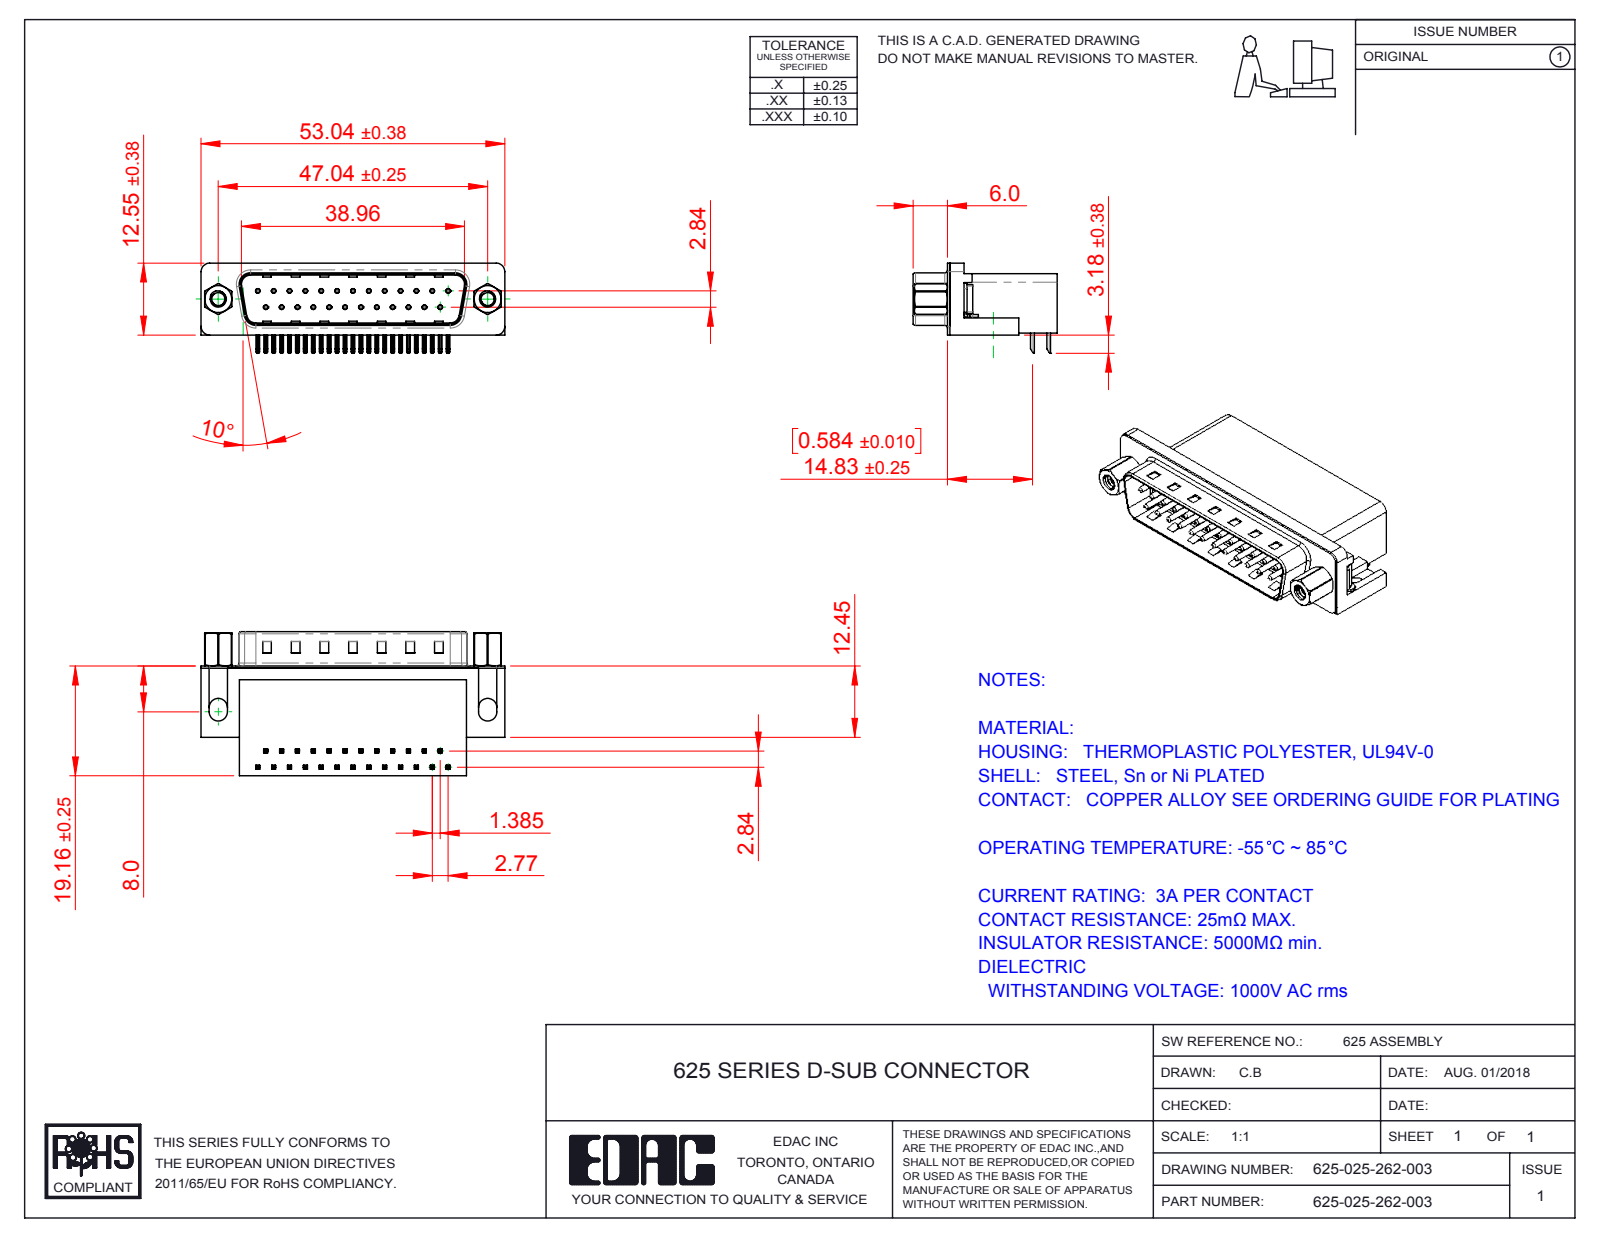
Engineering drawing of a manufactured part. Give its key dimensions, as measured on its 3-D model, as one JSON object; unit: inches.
{"part_name": "625 4-40 Threaded Rivet; 625 Contact Bottom; 625 Contact Top; 625 Non Board Mount (+4 more)", "step_written_by": "SolidWorks 2016 (CONFIG_CONTROL_DESIGN)", "units": "inches", "bodies": {"solids": 33, "faces": 2389, "planar": 1429, "cylindrical": 729, "other": 231}, "overall_size": [2.088, 0.991, 0.619], "volume_in3": 0.571, "surface_area_in2": 14.28, "round_holes": [[0.014, 25], [0.031, 25], [0.089, 2], [0.09, 2], [0.157, 2], [0.189, 2], [0.197, 2]], "round_bosses_or_shafts": [[0.03, 25], [0.193, 2], [0.187, 2], [0.154, 2], [0.11, 2]], "partial_cylinders_radius": [[0.01, 108], [0.005, 50], [0.039, 16], [0.02, 9], [0.063, 8], [0.059, 7], [0.035, 4], [0.079, 4]], "face_to_face_distances": [0.016, 0.407, 0.739, 0.083, 0.345, 0.412, 0.428, 0.067, 0.754, 0.398], "hole_center_spacings": [0.124, 0.109, 0.436, 0.218, 0.327, 0.198, 0.545, 0.294]}
